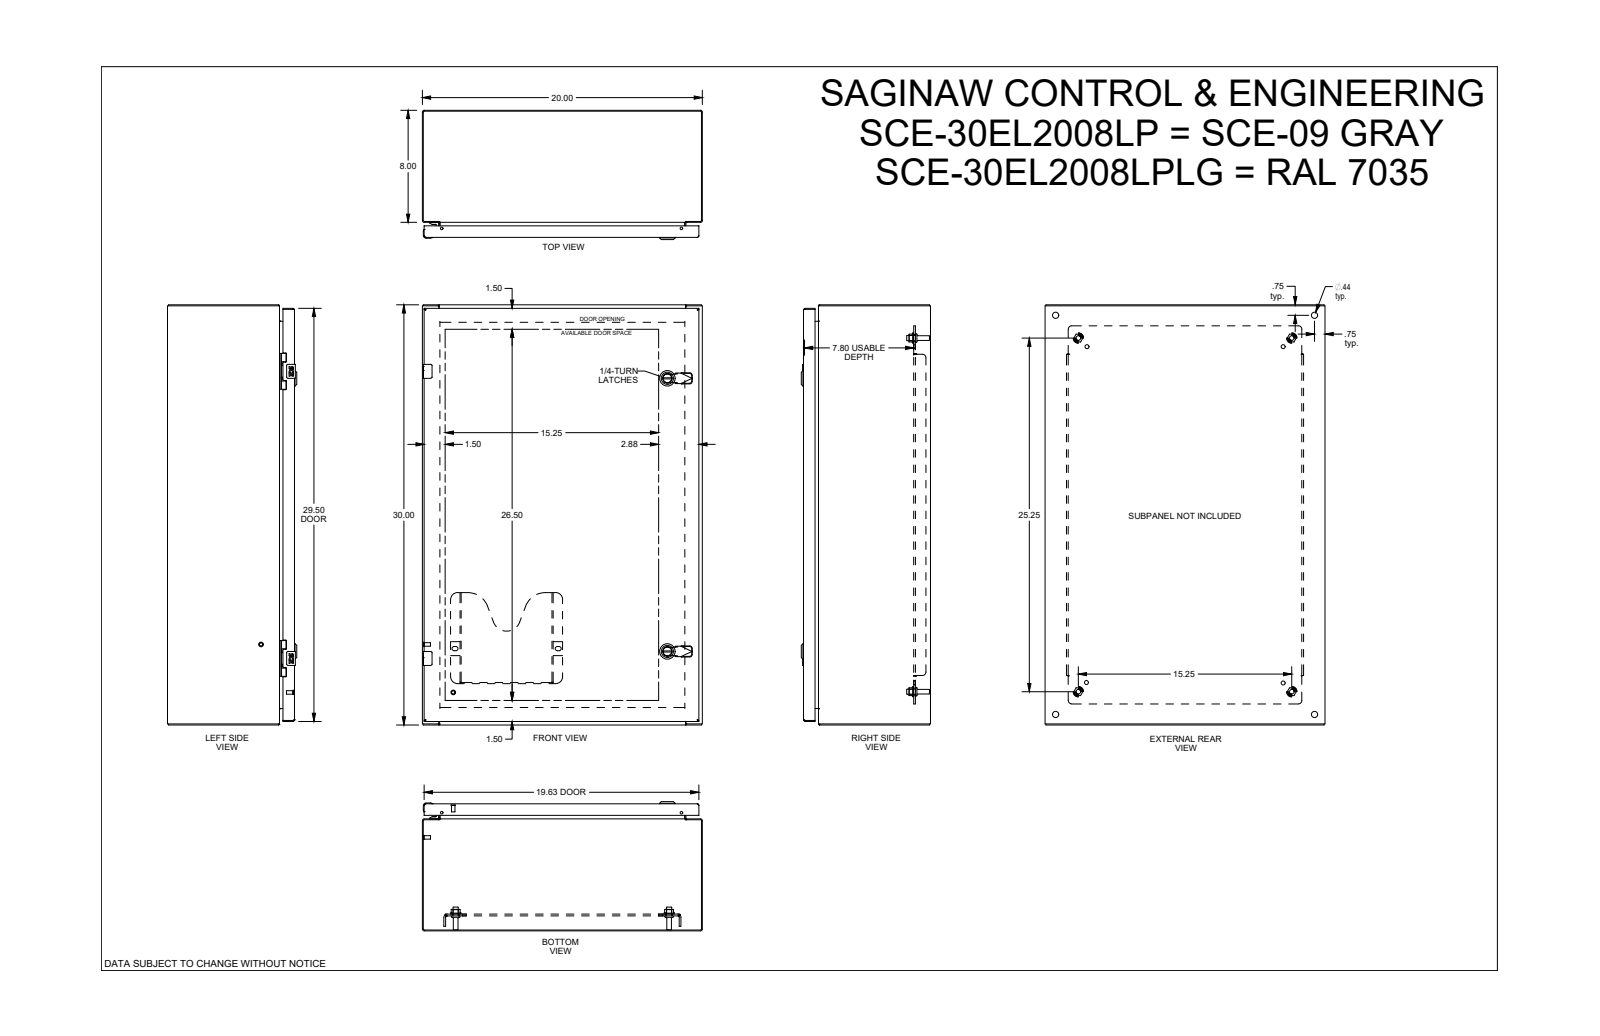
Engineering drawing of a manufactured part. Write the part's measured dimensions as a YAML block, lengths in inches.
part_name: "SCE-30EL2008LP"
step_written_by: "SolidWorks 2021 (AUTOMOTIVE_DESIGN)"
units: inches
bodies: {solids: 47, faces: 2811, planar: 1105, cylindrical: 848, other: 858}
overall_size: [30, 20, 9.23]
volume: 240.7
surface_area: 5797
round_holes:
  - {diameter: 0.172, count: 4}
  - {diameter: 0.205, count: 4}
  - {diameter: 0.244, count: 4}
  - {diameter: 0.266, count: 4}
  - {diameter: 0.281, count: 4}
  - {diameter: 0.367, count: 4}
  - {diameter: 0.375, count: 4}
  - {diameter: 0.437, count: 4}
  - {diameter: 0.5, count: 4}
  - {diameter: 0.04, count: 2}
  - {diameter: 0.188, count: 2}
  - {diameter: 0.197, count: 2}
round_bosses_or_shafts:
  - {diameter: 0.17, count: 6}
  - {diameter: 0.366, count: 4}
  - {diameter: 0.332, count: 4}
  - {diameter: 0.25, count: 4}
  - {diameter: 0.248, count: 4}
  - {diameter: 0.24, count: 4}
  - {diameter: 0.196, count: 3}
  - {diameter: 1.102, count: 2}
partial_cylinders:
  - {radius: 0.012, count: 56}
  - {radius: 0.01, count: 28}
  - {radius: 0.015, count: 24}
  - {radius: 0.02, count: 20}
  - {radius: 0.04, count: 17}
  - {radius: 0.06, count: 13}
  - {radius: 0.029, count: 12}
  - {radius: 0.1, count: 12}
face_to_face_distances: [0.075, 0.06, 9.073, 8.998, 9.013, 8.938, 1, 0.125, 19.925, 1.2]
hole_center_spacings: [0.985, 20.5, 0.02, 0.493, 0.494, 0.875, 2.298, 4.493]
